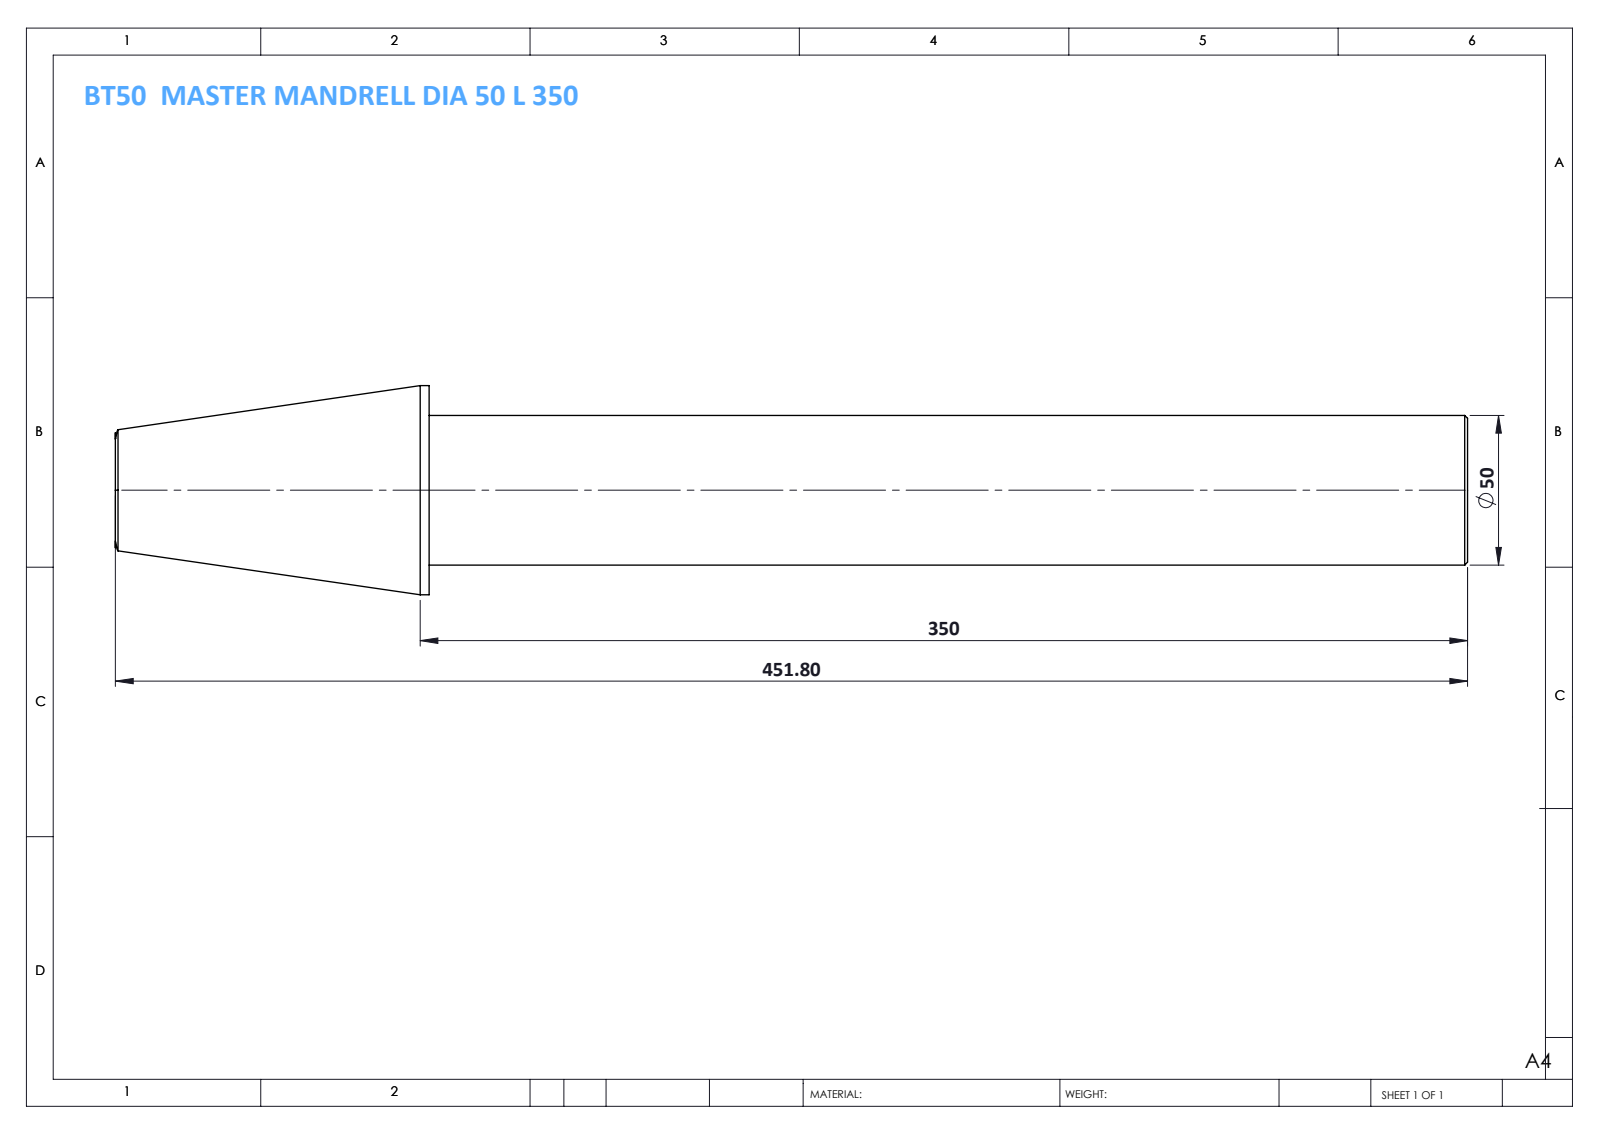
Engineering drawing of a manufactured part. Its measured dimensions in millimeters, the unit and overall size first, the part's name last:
Units: millimetres
Overall size (bounding box): 451.8 × 69.85 × 69.85
Round bosses / shafts (diameter × count): ⌀69.85 ×1, ⌀50 ×1
Main face-to-face distances: 347, 451.8, 104.8
Volume: 940 512 mm³ · Surface area: 77 909 mm²
Bodies: 1 solid, 13 faces (3 planar, 4 cylindrical, 6 other)
Part name (STEP PRODUCT): BT50 MASTER MANDRELL DIA 50 L 350
STEP written by: SolidWorks 2014 (CONFIG_CONTROL_DESIGN)
